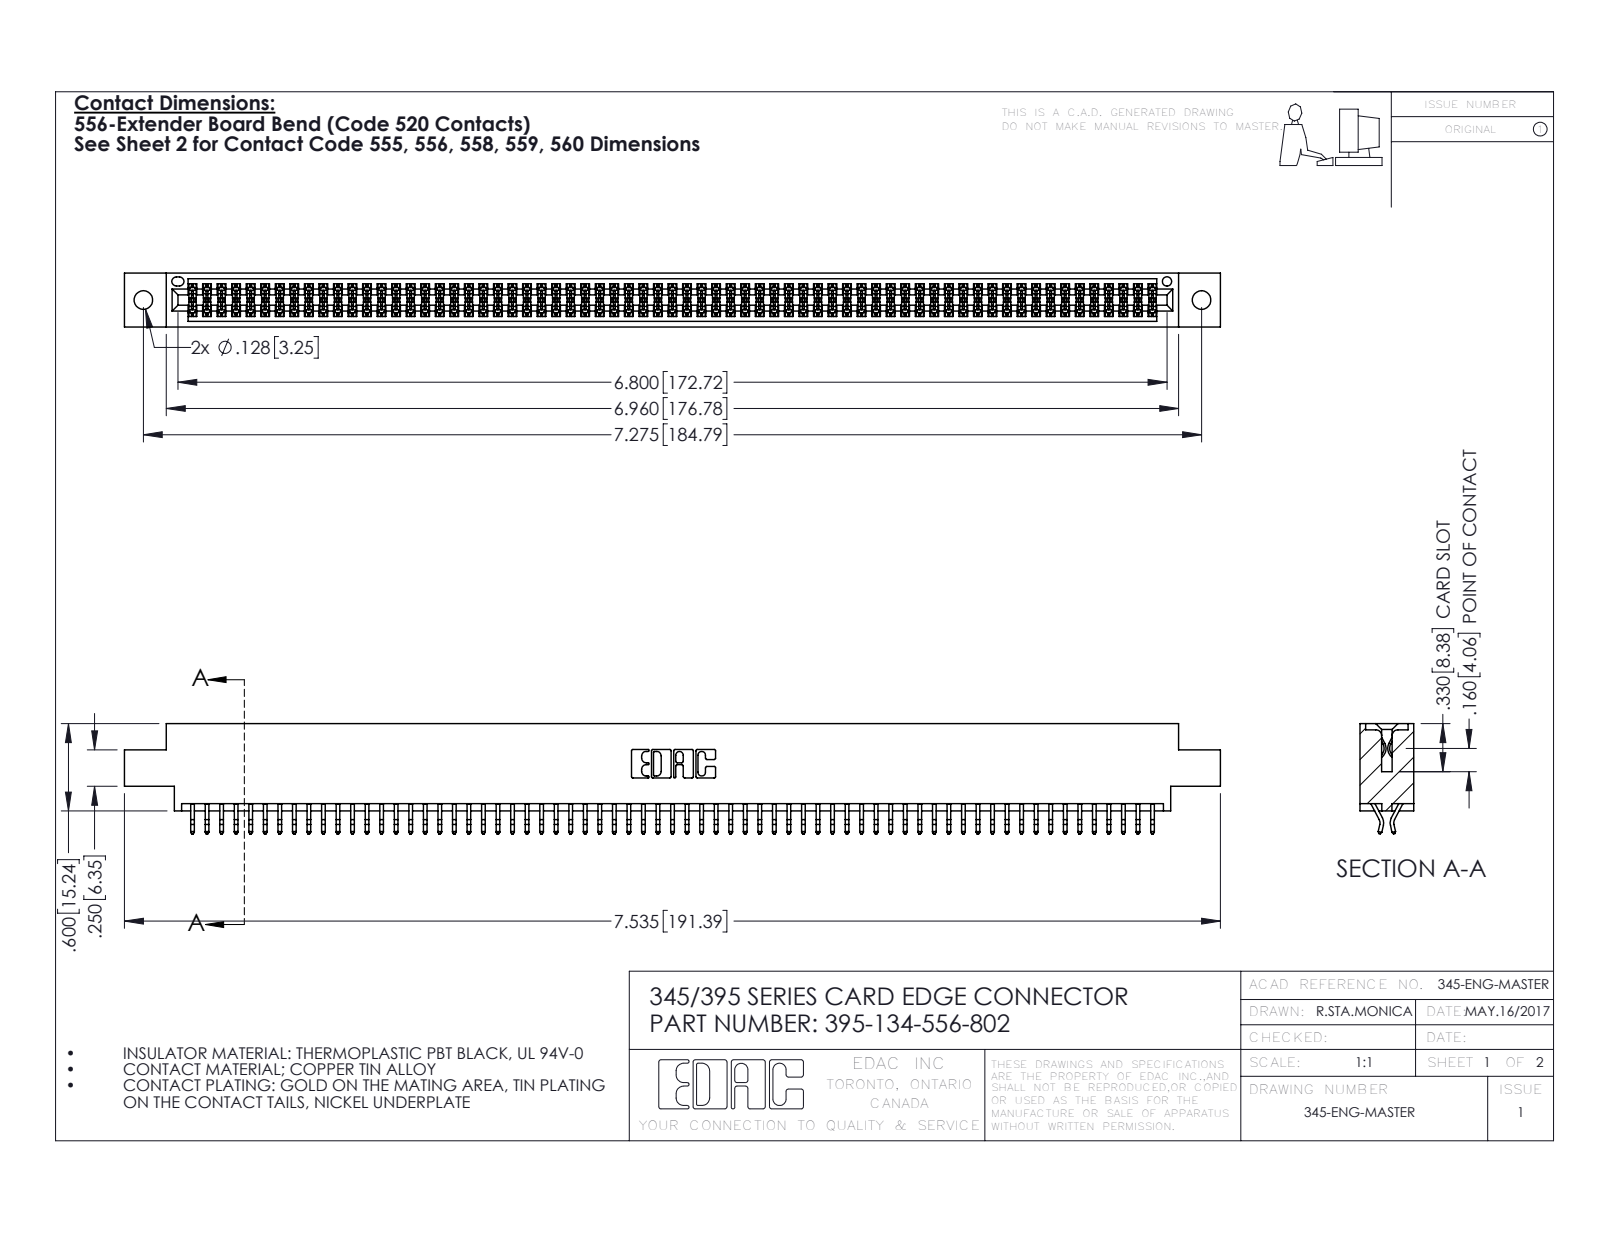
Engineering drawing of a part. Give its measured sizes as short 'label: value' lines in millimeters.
name: 345 Part_0.170 Offset - 0.128 Dia; 395-134-556-802; 345-292-001_556 Tail
written by: SolidWorks 2016 (CONFIG_CONTROL_DESIGN)
unit: mm
bodies: 135 solids, 7634 faces (5042 planar, 2592 cylindrical, 0 other)
size: 191.4 × 19.2 × 9.4
volume: 18 660 mm³; area: 27 830 mm²
holes: 2× ⌀3.3, 1× ⌀1.6
rounds: 201× R0.2, 22× R0.3, 6× R0.2, 6× R0.8, 3× R0.7, 2× R0.3, 2× R0.4, 2× R0.5
face distances: 7.6, 1.8, 9.4, 5.1, 0.6, 2.5, 6.9, 5.7, 4.4, 3.8
hole spacings: 6.9, 178.8, 184.8
